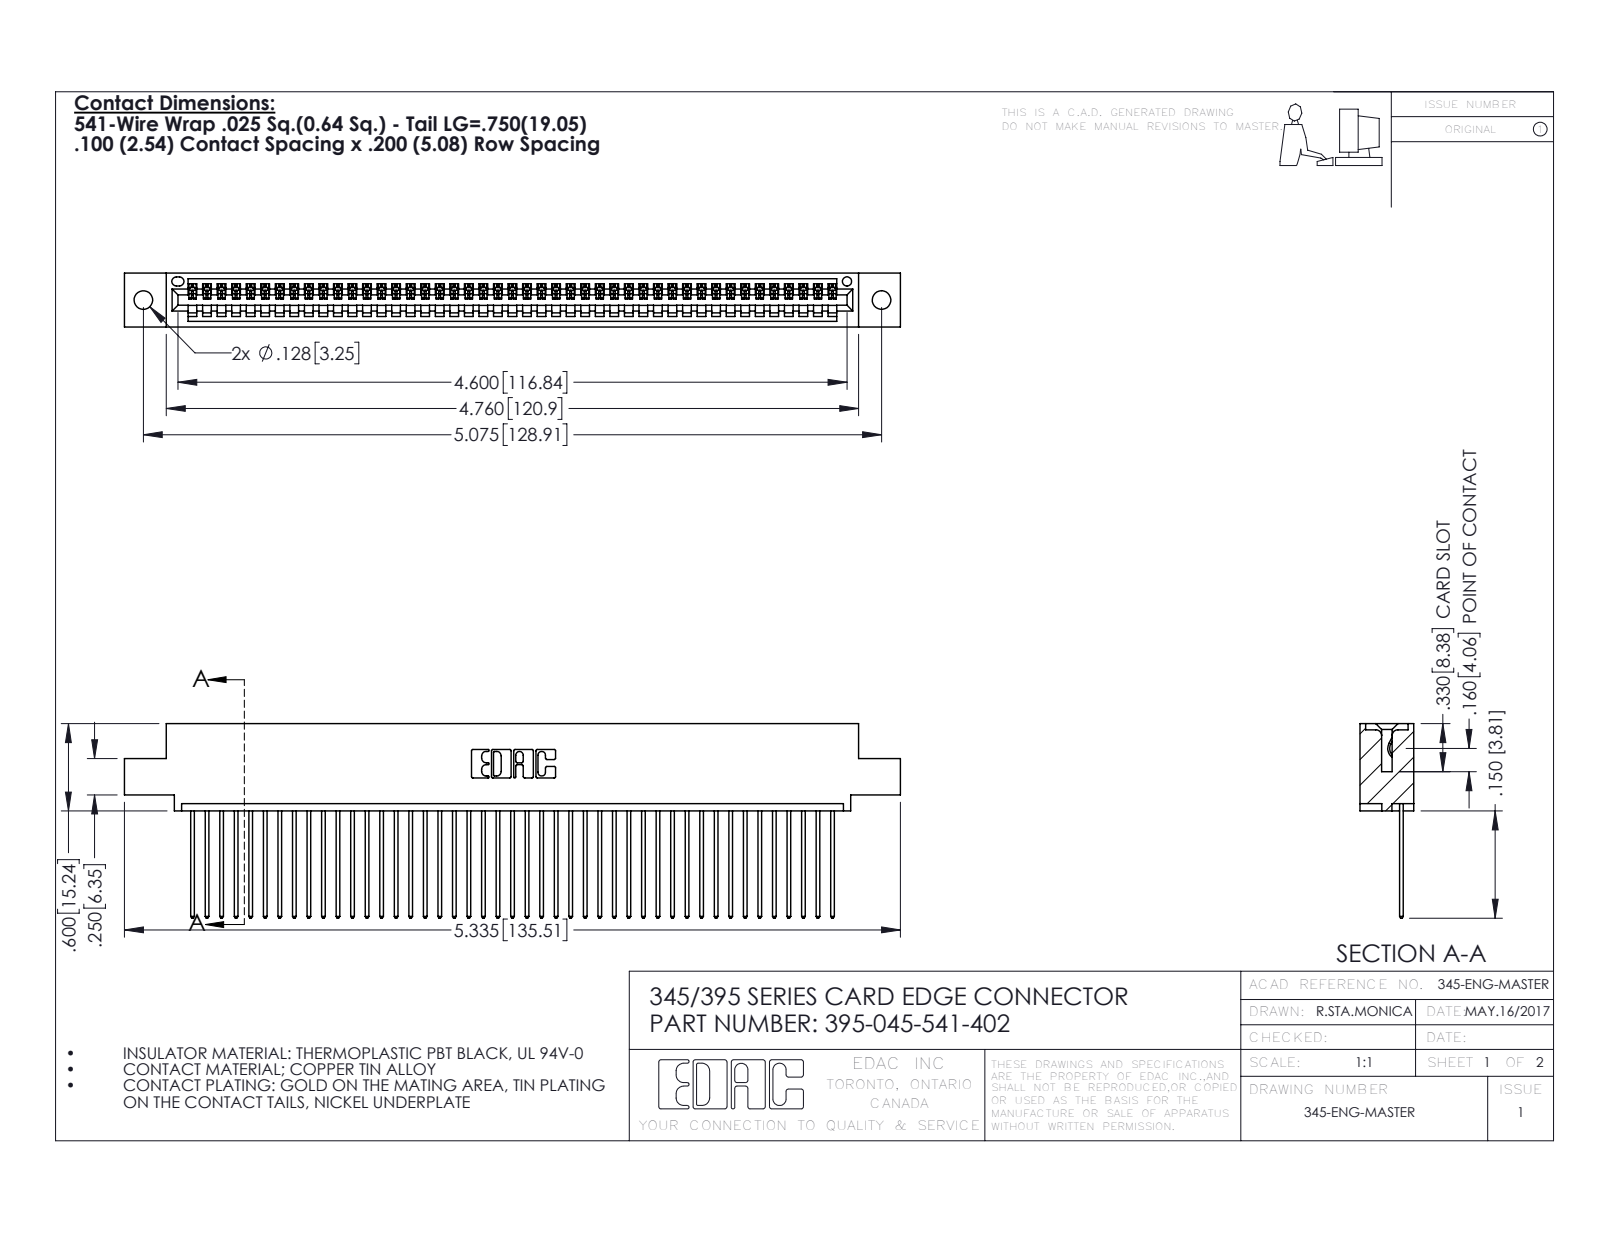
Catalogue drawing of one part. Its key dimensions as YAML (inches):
part_name: "345-292-001_345-293-141; 395-045-541-402; 345 Part_0.110 Offset - 0.128 Dia"
step_written_by: "SolidWorks 2016 (CONFIG_CONTROL_DESIGN)"
units: inches
bodies: {solids: 46, faces: 2740, planar: 1884, cylindrical: 856, other: 0}
overall_size: [5.335, 1.337, 0.37]
volume: 0.789
surface_area: 27.76
round_holes:
  - {diameter: 0.128, count: 2}
  - {diameter: 0.064, count: 1}
partial_cylinders:
  - {radius: 0.006, count: 90}
  - {radius: 0.01, count: 90}
  - {radius: 0.01, count: 22}
  - {radius: 0.007, count: 6}
  - {radius: 0.031, count: 6}
  - {radius: 0.026, count: 3}
  - {radius: 0.031, count: 2}
  - {radius: 0.04, count: 2}
face_to_face_distances: [0.072, 0.298, 0.098, 0.272, 0.025, 0.37, 0.2, 0.225, 0.149, 0.072]
hole_center_spacings: [0.27, 4.839, 5.075]
